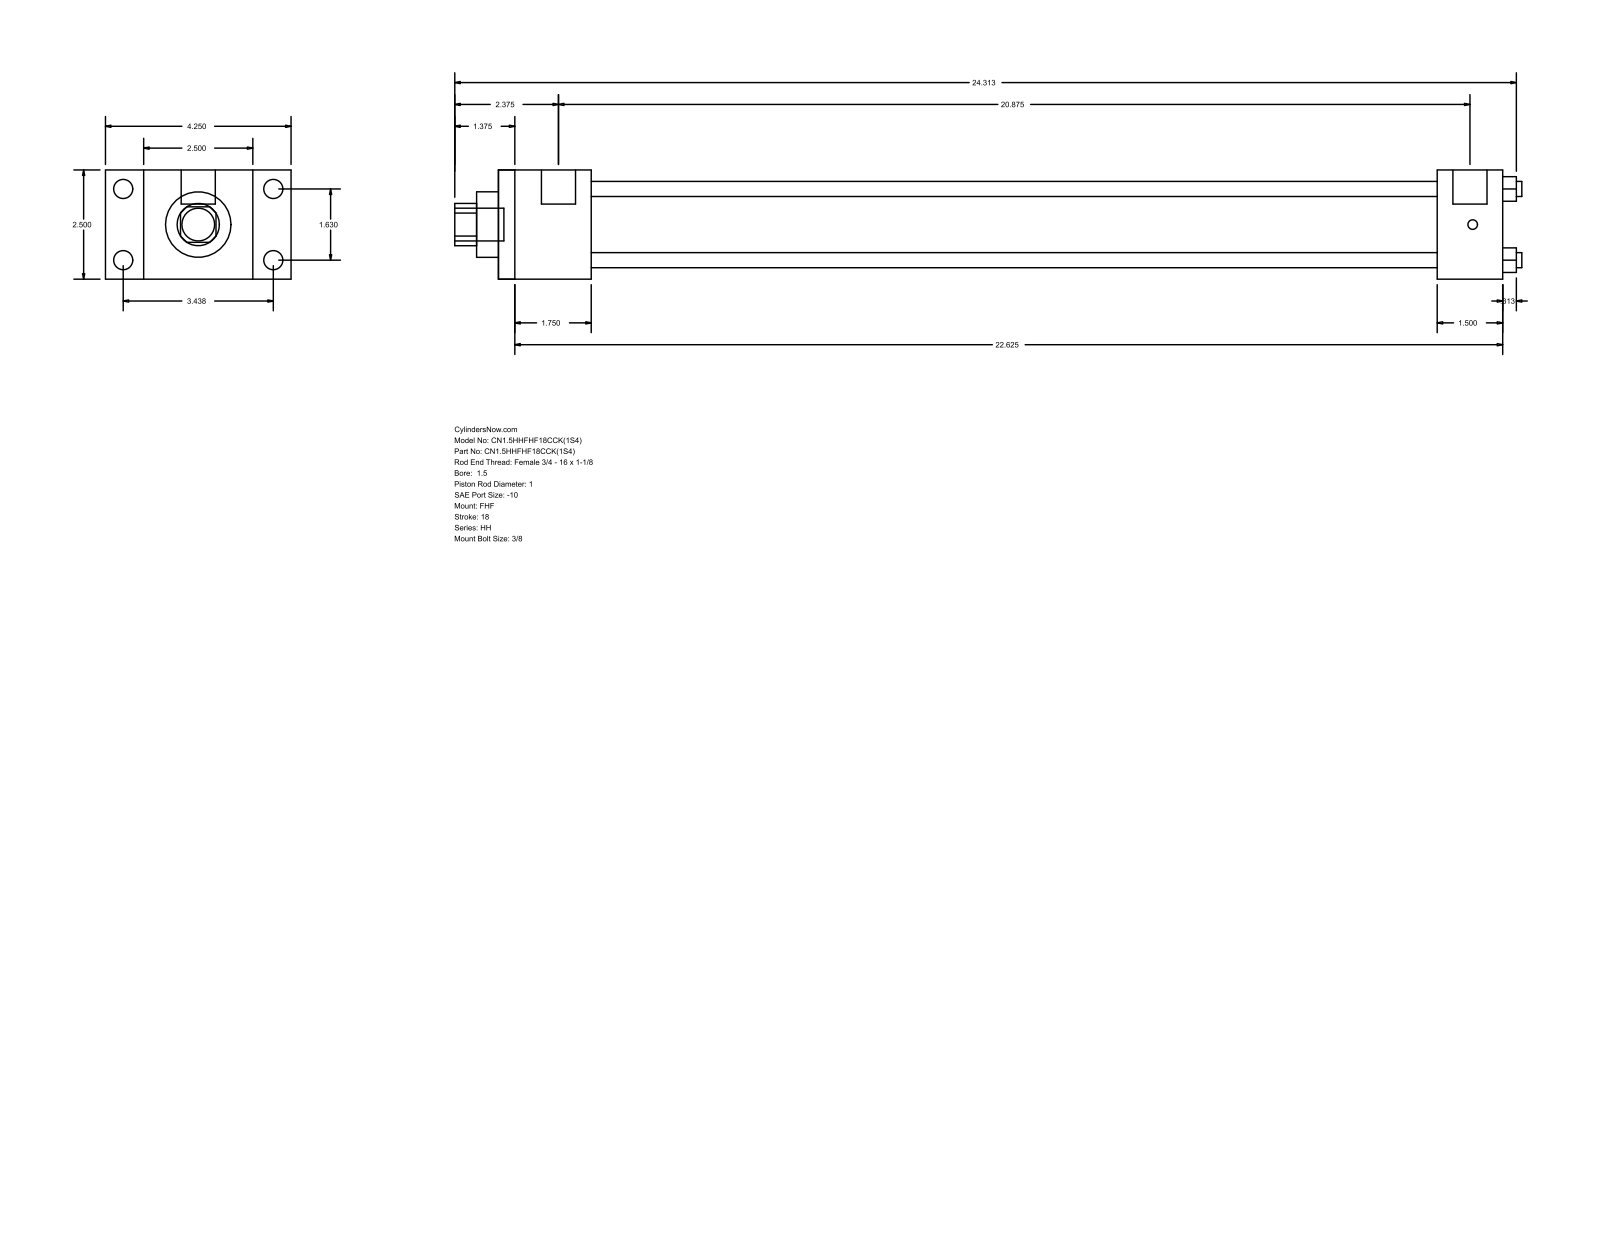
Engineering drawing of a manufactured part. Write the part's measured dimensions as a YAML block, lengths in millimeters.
part_name: "HH_FHF__0150_1"
step_written_by: "GSSL Pune (CONFIG_CONTROL_DESIGN)"
units: millimeters
bodies: {solids: 0, faces: 88, planar: 60, cylindrical: 28, other: 0}
overall_size: [620.71, 107.95, 63.5]
round_holes:
  - {diameter: 8.76, count: 4}
  - {diameter: 25.4, count: 1}
  - {diameter: 38.1, count: 1}
  - {diameter: 44.45, count: 1}
round_bosses_or_shafts:
  - {diameter: 11.13, count: 4}
  - {diameter: 5.56, count: 4}
  - {diameter: 19.84, count: 2}
  - {diameter: 19.05, count: 1}
partial_cylinders:
  - {radius: 12.29, count: 1}
face_to_face_distances: [63.5, 22.23, 85.73, 53.98, 107.96, 584.2, 530.22, 546.1, 492.12, 38.1]
hole_center_spacings: [29.27, 41.4, 58.55]
